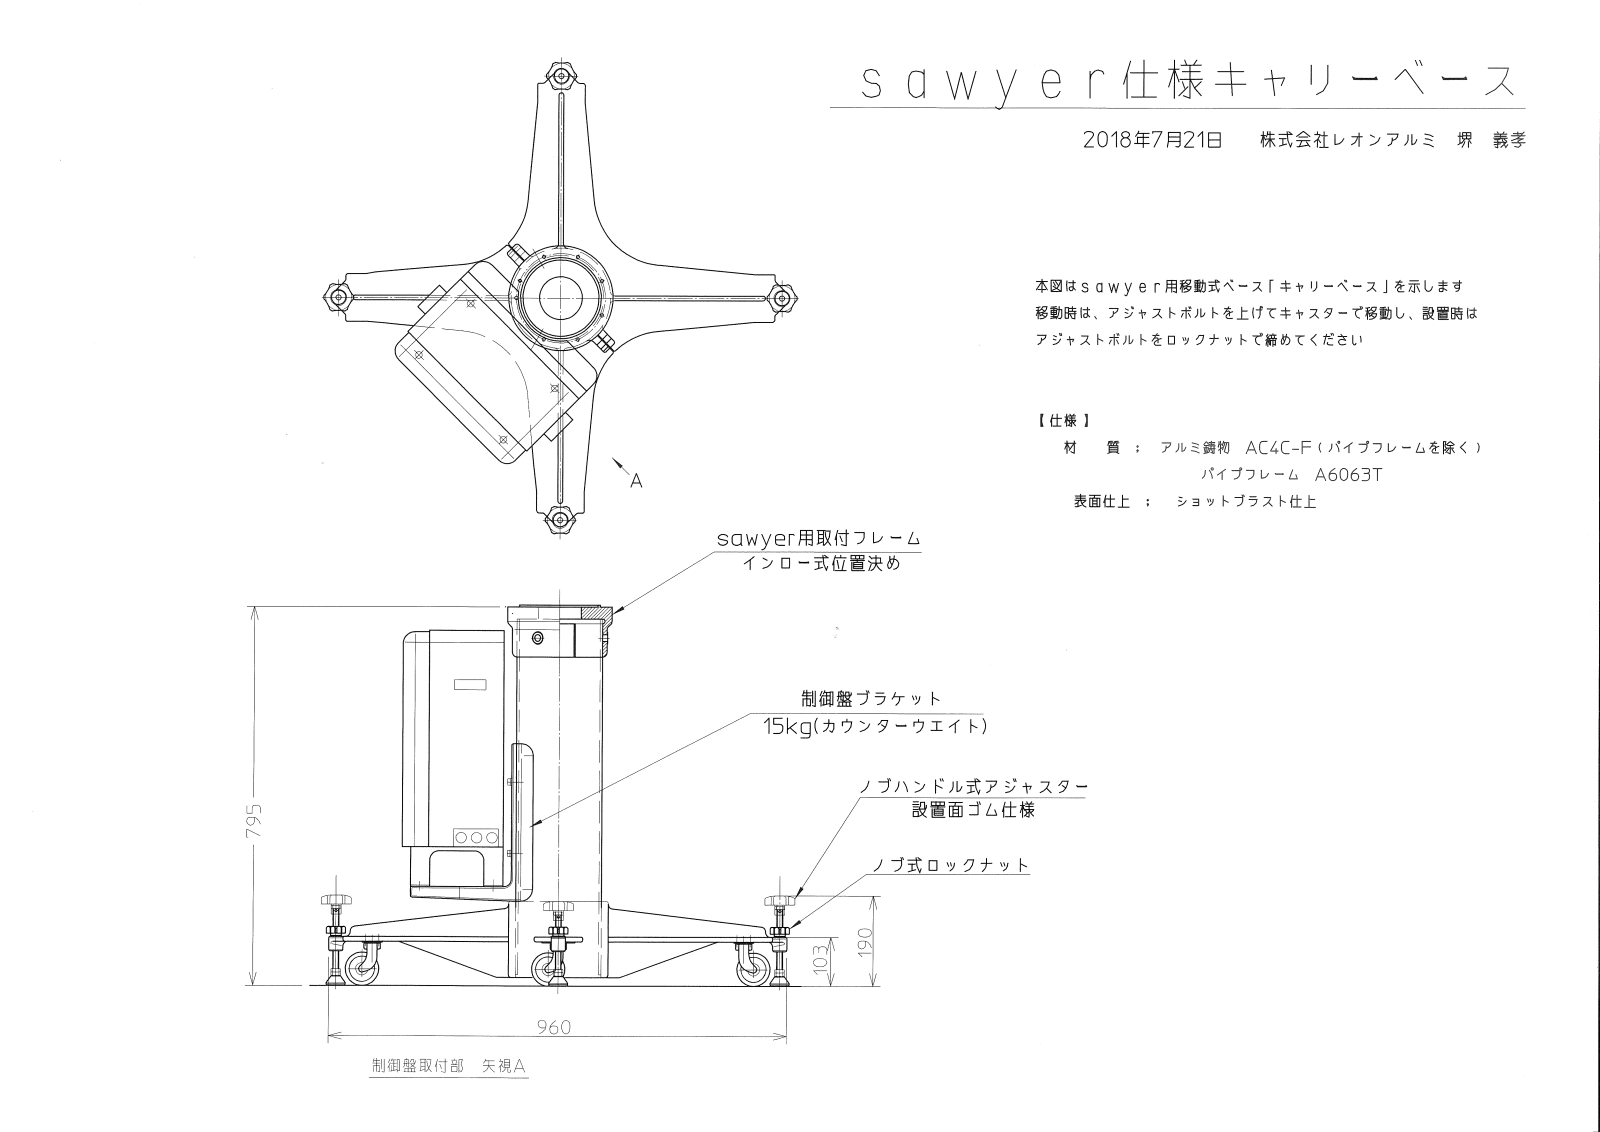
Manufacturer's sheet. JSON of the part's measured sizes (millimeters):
{"part_name": "パーツ55; パーツ196; パーツ259; パーツ348 (+7 more)", "step_written_by": "Spatial InterOp 3D (automotive_design)", "units": "millimeters", "bodies": {"solids": 82, "faces": 5147, "planar": 2127, "cylindrical": 933, "other": 2087}, "overall_size": [799.25, 718.86, 718.86], "volume_mm3": 15170000, "surface_area_mm2": 2544000, "round_holes": [[6, 16], [6.5, 16], [13, 11], [15, 8], [52, 8], [2, 4], [4, 4], [4.5, 4], [12, 4], [18, 4], [22.9, 4], [23, 4]], "round_bosses_or_shafts": [[11.7, 23], [12.7, 16], [21, 11], [30, 10], [26, 7], [40, 4], [39, 4], [34, 4]], "partial_cylinders_radius": [[2, 94], [0.5, 64], [10, 52], [1.8, 48], [5, 48], [6, 32], [1.5, 30], [3, 14]], "face_to_face_distances": [10, 115.33, 105.33, 45, 699, 689, 583.67, 75, 85, 676], "hole_center_spacings": [31.7, 744.24, 505.97, 546.71, 772.81, 758, 31.71, 566.19]}
